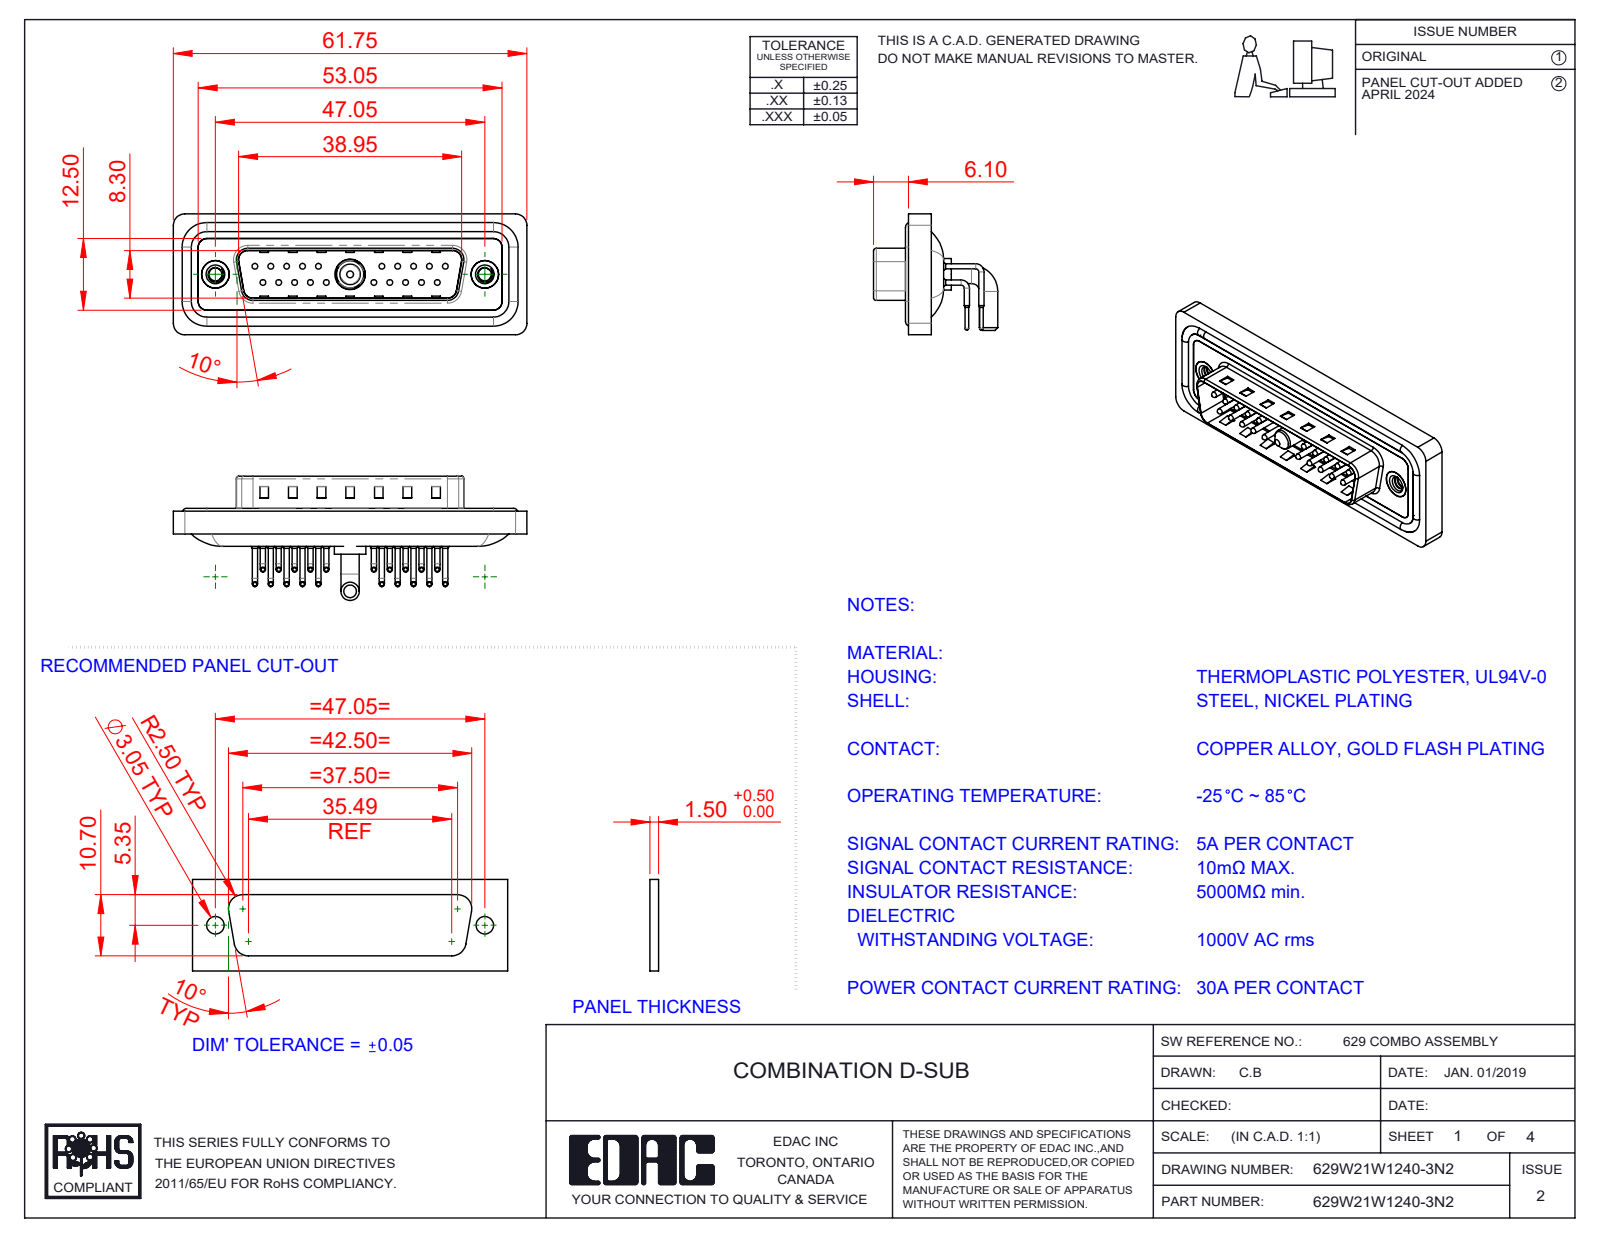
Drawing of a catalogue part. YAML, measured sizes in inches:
part_name: "629Combo Shell Rear_25 Contacts; 629Combo Housing_21W1; 629Combo Shell Front_25 Contacts; 629Combo Waterproof Housing_25 Contacts (+5 more)"
step_written_by: "SolidWorks 2023 (CONFIG_CONTROL_DESIGN)"
units: inches
bodies: {solids: 29, faces: 2726, planar: 1499, cylindrical: 929, other: 298}
overall_size: [2.431, 0.854, 0.831]
volume: 0.455
surface_area: 19.75
round_holes:
  - {diameter: 0.03, count: 20}
  - {diameter: 0.063, count: 20}
  - {diameter: 0.079, count: 20}
  - {diameter: 0.089, count: 2}
  - {diameter: 0.157, count: 2}
  - {diameter: 0.189, count: 2}
  - {diameter: 0.197, count: 2}
  - {diameter: 0.191, count: 1}
  - {diameter: 0.209, count: 1}
round_bosses_or_shafts:
  - {diameter: 0.035, count: 40}
  - {diameter: 0.059, count: 20}
  - {diameter: 0.039, count: 20}
  - {diameter: 0.026, count: 20}
  - {diameter: 0.063, count: 4}
  - {diameter: 0.193, count: 2}
  - {diameter: 0.126, count: 2}
  - {diameter: 0.217, count: 1}
partial_cylinders:
  - {radius: 0.04, count: 20}
  - {radius: 0.059, count: 18}
  - {radius: 0.079, count: 18}
  - {radius: 0.02, count: 8}
  - {radius: 0.063, count: 8}
  - {radius: 0.01, count: 4}
  - {radius: 0.024, count: 4}
  - {radius: 0.026, count: 4}
face_to_face_distances: [0.016, 0.114, 0.031, 0.161, 0.043, 0.083, 0.063, 0.177, 0.059, 0.098]
hole_center_spacings: [0.124, 0.109, 0.218, 0.327, 0.198, 0.763, 0.826, 0.872]
